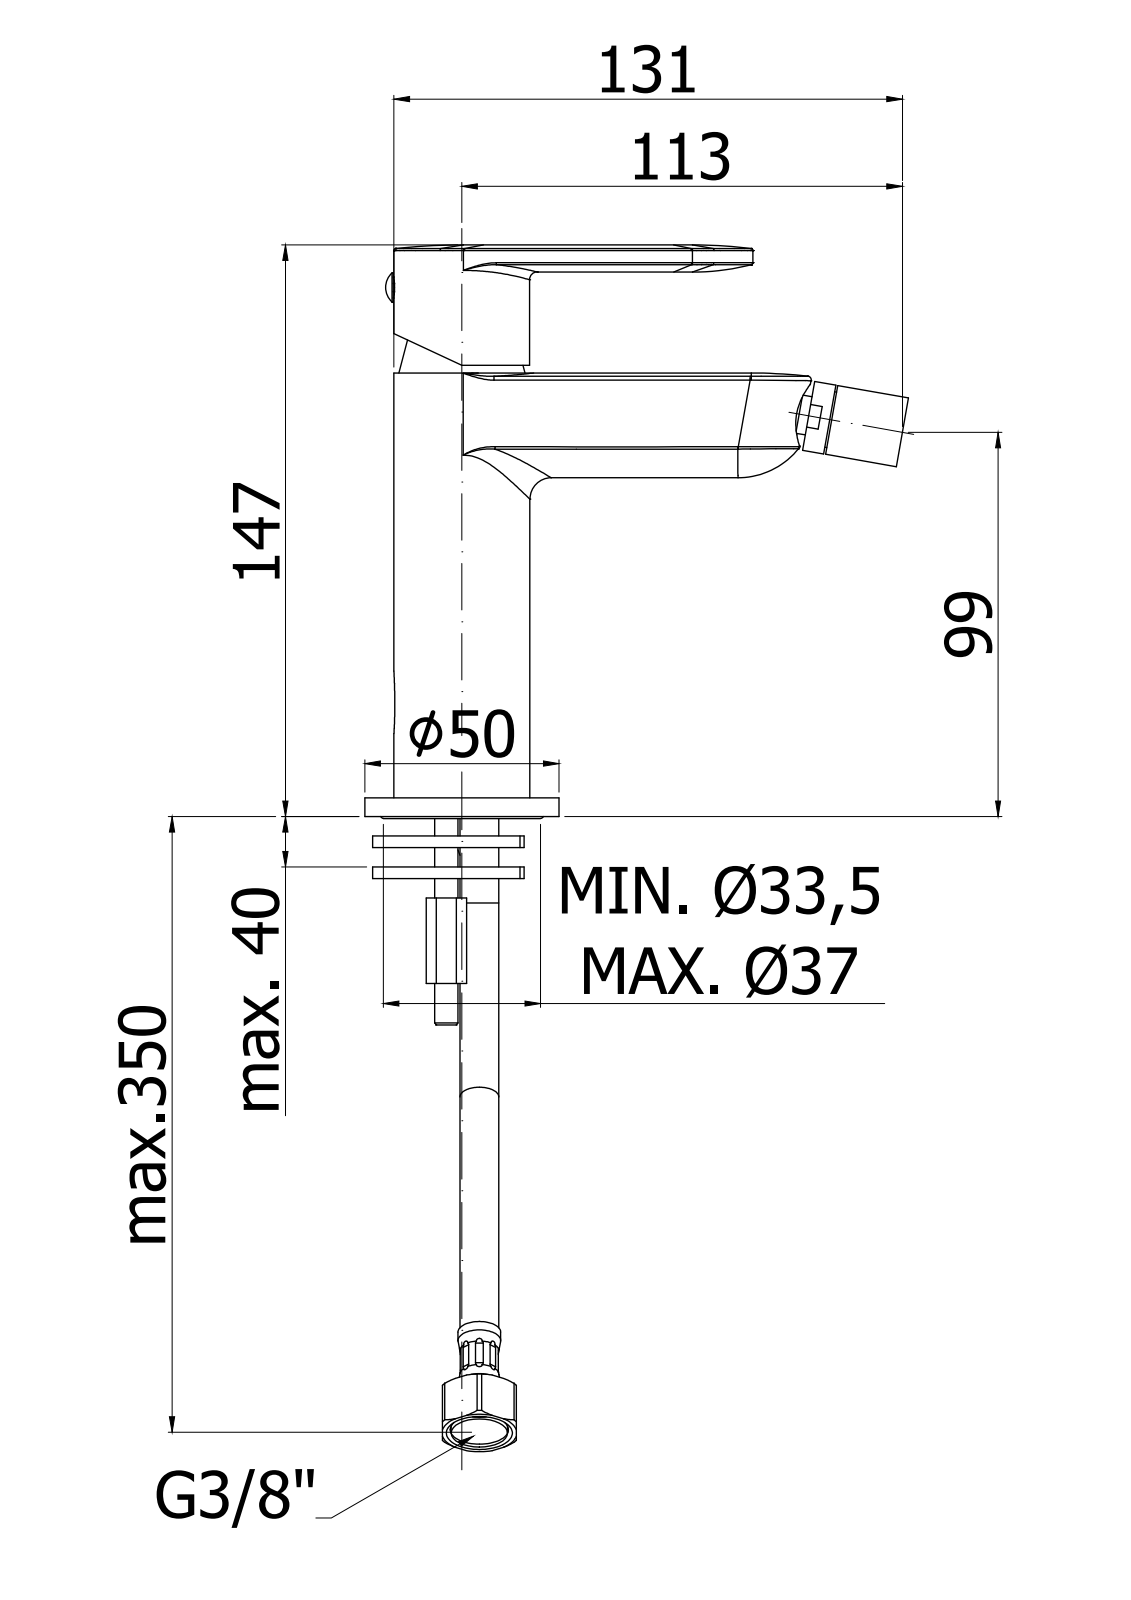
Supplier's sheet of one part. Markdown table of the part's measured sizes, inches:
| quantity | value |
| --- | --- |
| part name | CA131CR |
| STEP written by | CREO PARAMETRIC BY PTC INC, 2020044 (CONFIG_CONTROL_DESIGN) |
| units | inches |
| bodies | 2 solids, 176 faces (48 planar, 50 cylindrical, 78 other) |
| overall size | 5.745 × 5.494 × 1.969 |
| volume | 12.67 in³ |
| surface area | 64.47 in² |
| round holes (diameter × count) | 0.118 × 1, 0.177 × 1, 0.657 × 1, 0.976 × 1, 1.031 × 1, 1.102 × 1 |
| round bosses / shafts (diameter × count) | 1.969 × 1, 1.417 × 1, 1.378 × 1, 0.709 × 1, 0.63 × 1, 0.571 × 1, 0.394 × 1, 0.299 × 1 |
| partial cylindrical surfaces (radius × count) | 0.118 × 4, 0.138 × 1, 0.63 × 1 |
| main face-to-face distances | 0.157, 4.488, 4.331, 5.627, 5.469, 1.139, 0.098, 0.453, 0.354, 0.965 |
